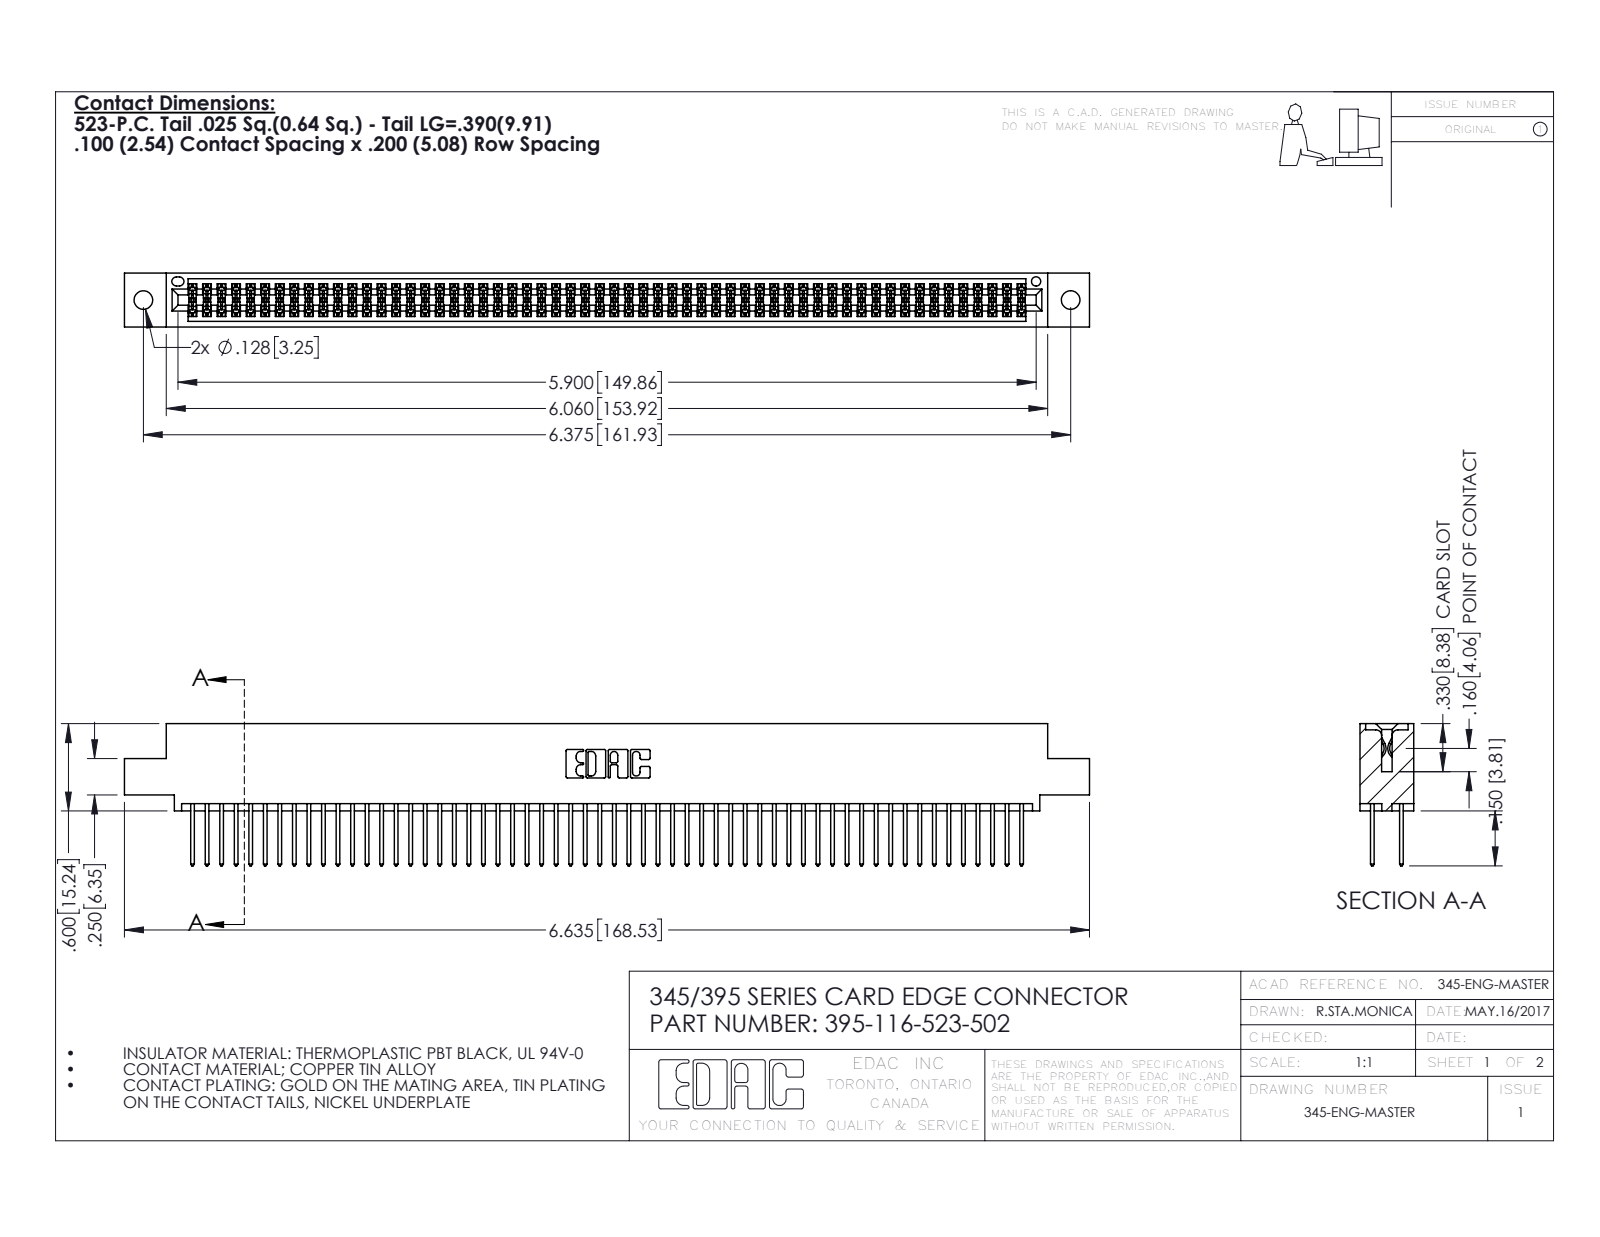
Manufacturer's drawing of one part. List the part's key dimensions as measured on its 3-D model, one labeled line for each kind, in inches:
Part name (STEP PRODUCT): 395-116-523-502; 345-292-001_345-293-123; 345 Part_0.110 Offset - 0.128 Dia
STEP written by: SolidWorks 2016 (CONFIG_CONTROL_DESIGN)
Units: inches
Bodies: 117 solids, 5930 faces (3912 planar, 2018 cylindrical, 0 other)
Overall size (bounding box): 6.635 × 0.977 × 0.37
Volume: 1.016 in³ · Surface area: 40 in²
Round holes (diameter × count): ⌀0.128 ×2, ⌀0.064 ×1
Partial cylindrical surfaces — rounded edges, fillets, slot ends (radius × count): R0.006 ×174, R0.01 ×116, R0.01 ×22, R0.007 ×6, R0.031 ×6, R0.026 ×3, R0.014 ×2, R0.019 ×2
Main face-to-face distances: 0.298, 0.072, 0.2, 0.098, 0.272, 0.025, 0.37, 0.225, 0.175, 0.149
Hole centre spacings: 0.27, 6.139, 6.375
